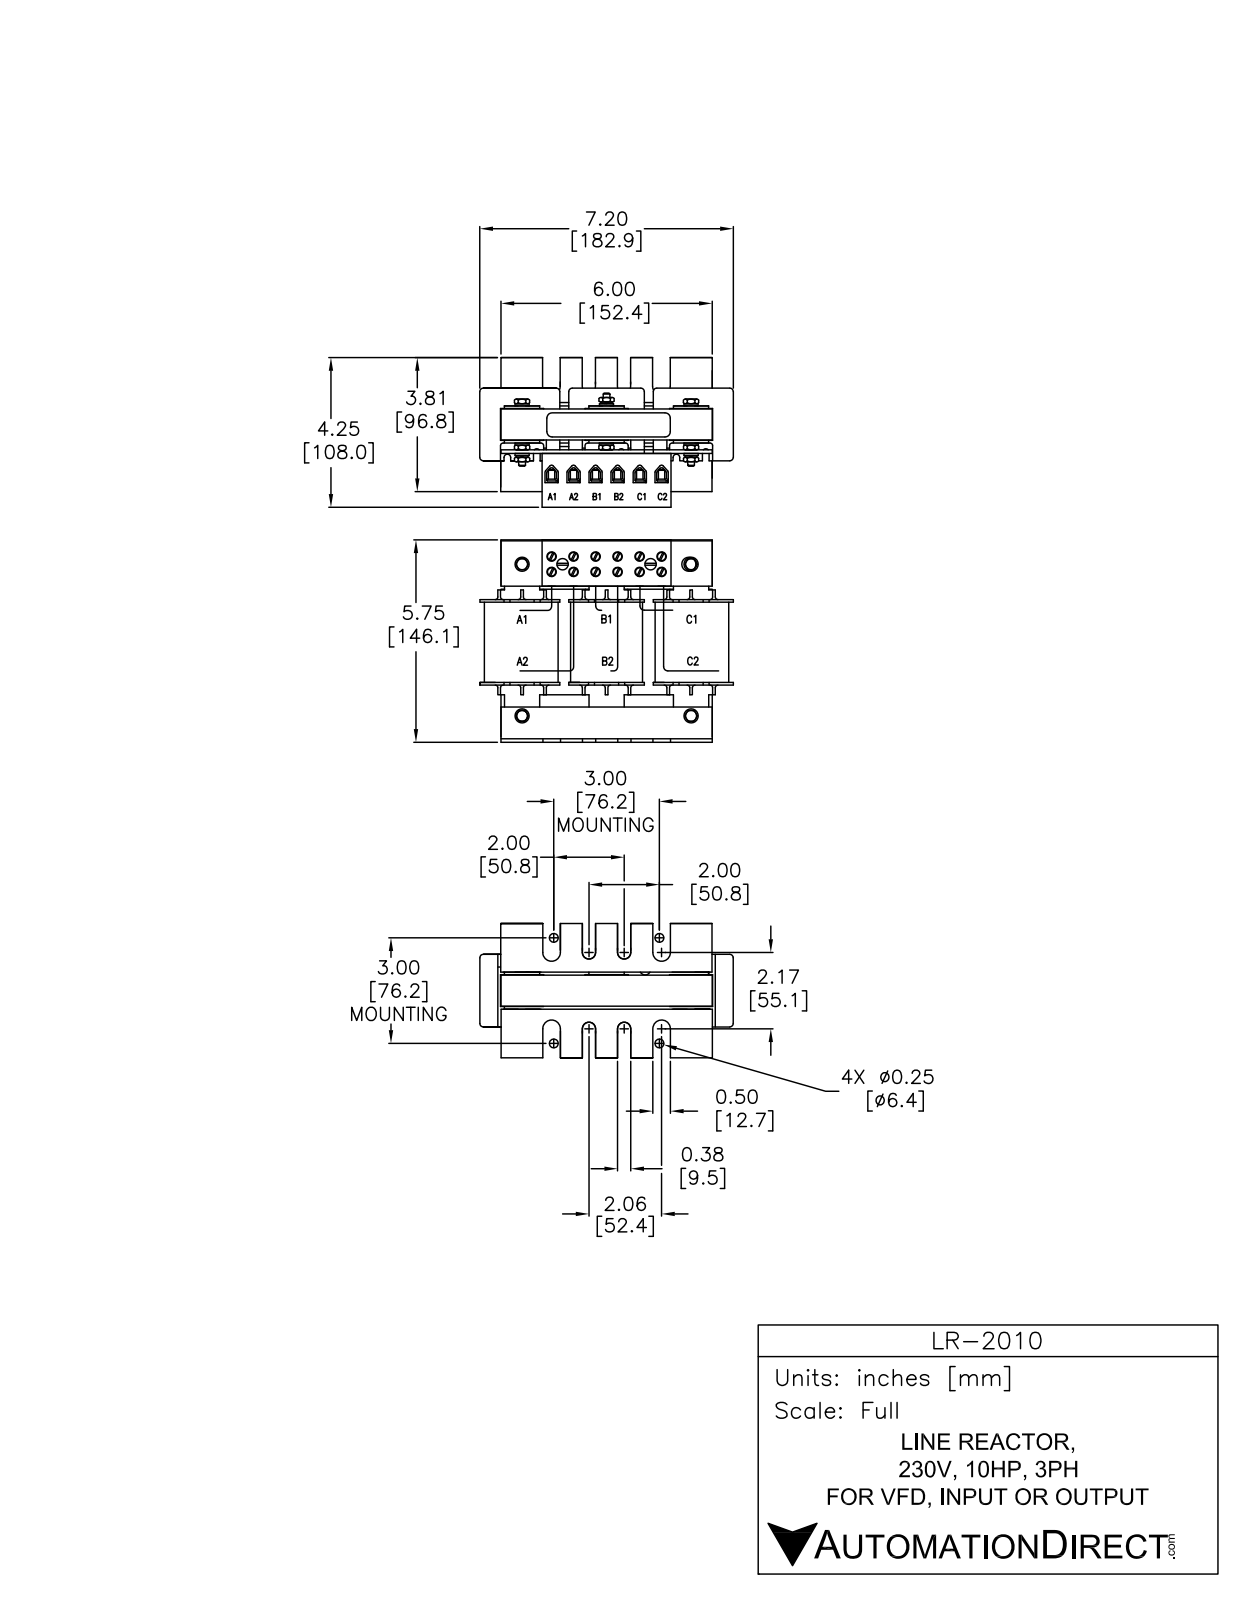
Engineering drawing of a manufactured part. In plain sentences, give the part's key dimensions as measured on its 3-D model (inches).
The part is named "LR-2010". Its 3-D file was written by "SolidWorks 2011 (AUTOMOTIVE_DESIGN)". It is 34 solids with 1041 faces: 767 planar, 242 cylindrical and 32 other. Overall it measures 7.008 by 5.619 by 3.907 inches. Its volume is 51.71 cubic inches and its surface area 302.9 square inches. Round holes: 12 of diameter 0.276, 5 of diameter 0.305. Round bosses or shafts: 5 of diameter 0.472, 5 of diameter 0.413, 2 of diameter 0.305, 2 of diameter 0.183, 1 of diameter 0.184, 1 of diameter 0.183, 1 of diameter 0.183. Partial cylindrical surfaces (rounded edges, fillets, slot ends): 24 of radius 0.106, 12 of radius 0.197, 12 of radius 0.276, 6 of radius 0.089, 4 of radius 0.059, 4 of radius 0.177, 4 of radius 0.246, 2 of radius 0.128. The main face-to-face distances are 0.079, 0.364, 2.441, 1.329, 1.407, 0.108, 0.344, 0.266, 0.443, 0.187. The hole center spacings are 0.63, 1.26, 0.376, 0.394, 0.77, 0.96, 0.981, 1.335.
